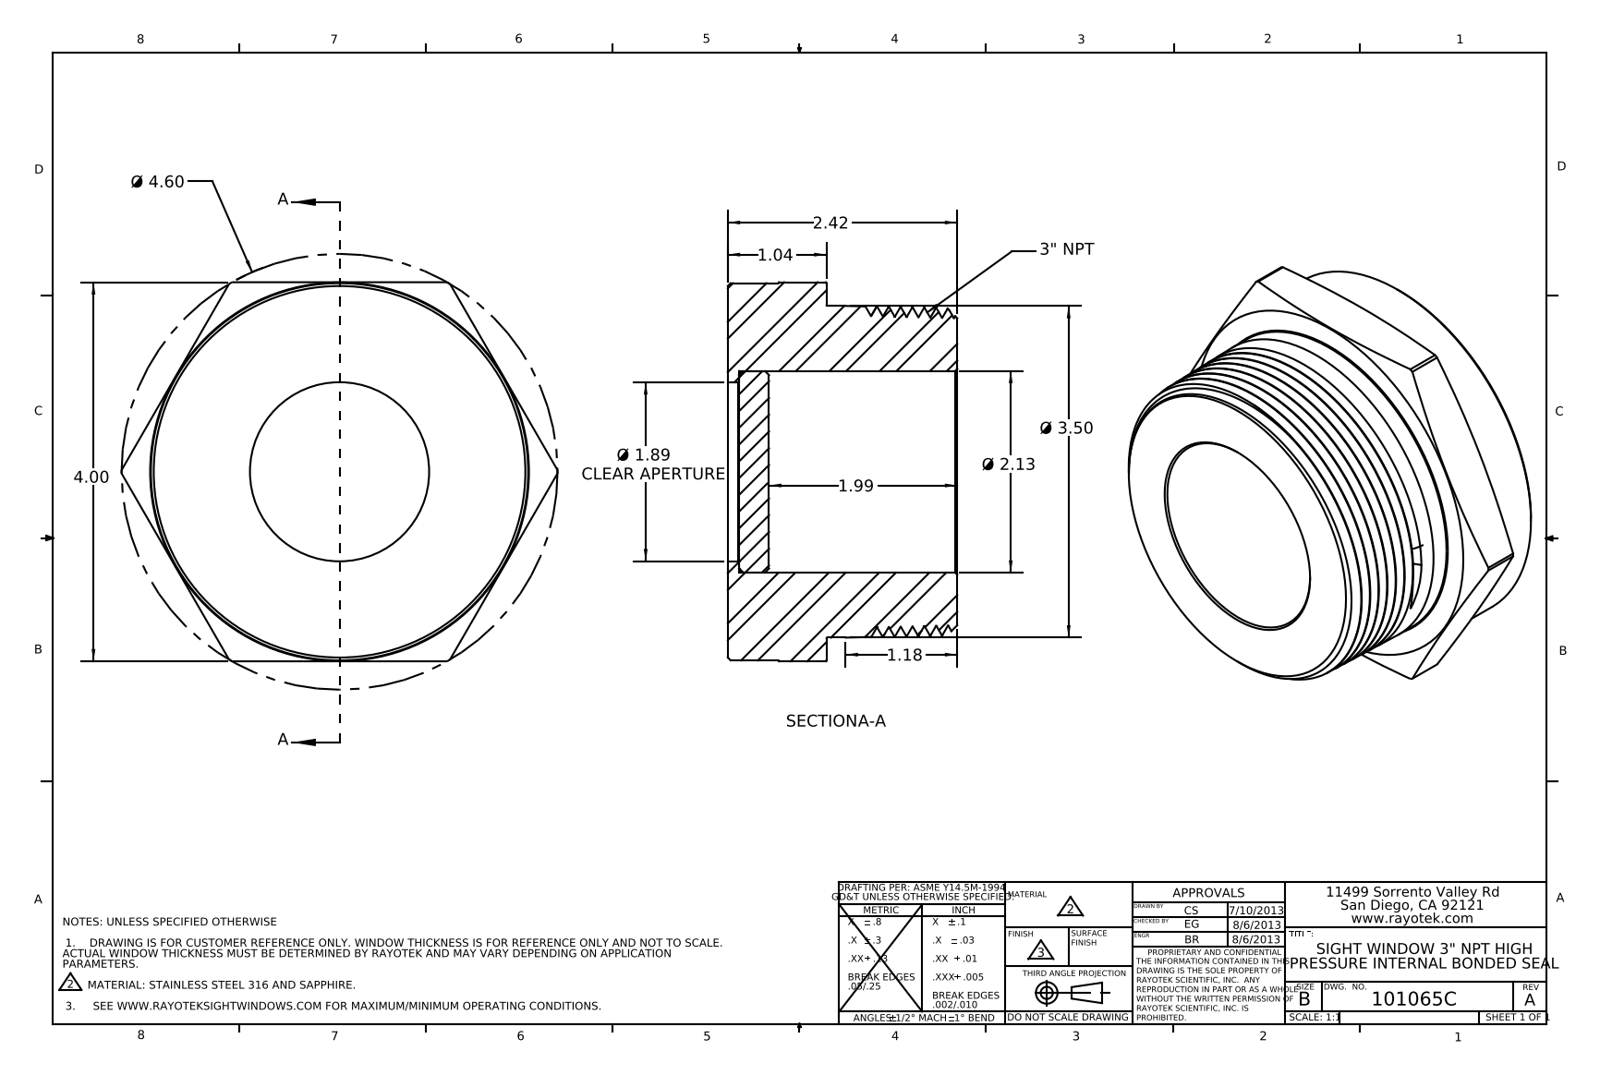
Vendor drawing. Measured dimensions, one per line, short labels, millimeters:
name: 101065; 402065; 403065
written by: SolidWorks 2012 (AUTOMOTIVE_DESIGN)
unit: mm
bodies: 2 solids, 73 faces (15 planar, 17 cylindrical, 41 other)
size: 116.8 × 101.6 × 61.5
volume: 306 900 mm³; area: 52 810 mm²
holes: 1× ⌀48, 1× ⌀54.1
bosses: 1× ⌀101.1, 1× ⌀88.9, 1× ⌀53.8
rounds: 1× R58.4
face distances: 61.5, 3, 58.4, 11, 8, 50.4, 101.6, 26.4, 23.4, 15.4
